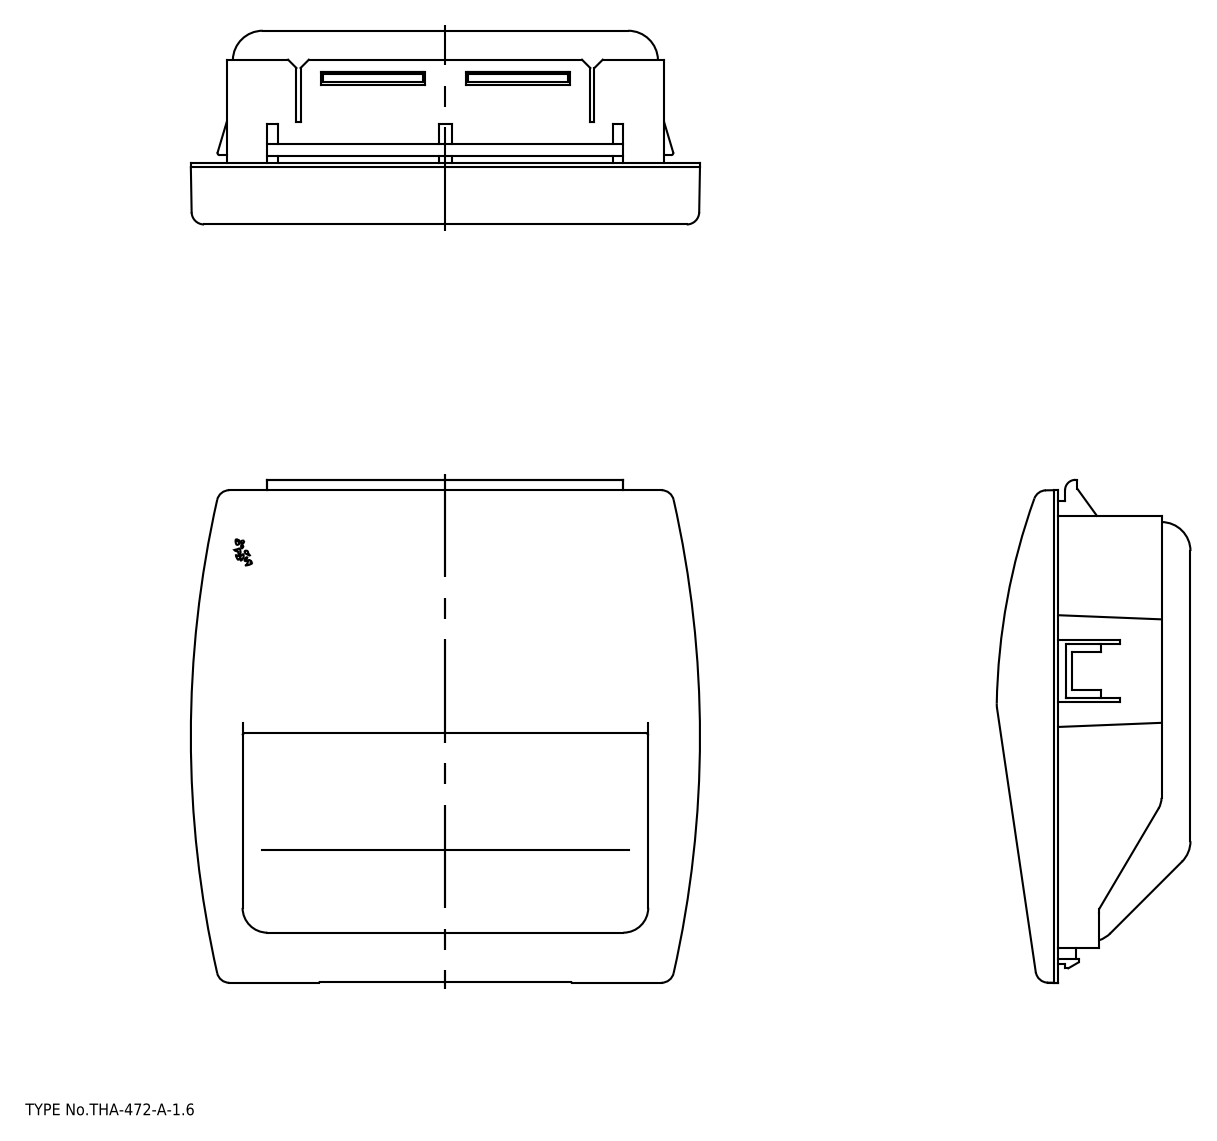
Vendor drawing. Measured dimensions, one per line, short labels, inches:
name: 0020; j10488b0010 2020-03-24; J10488B0030
written by: spGate 16.7.1 (AUTOMOTIVE_DESIGN)
unit: in
bodies: 3 solids, 703 faces (275 planar, 264 cylindrical, 164 other)
size: 4.843 × 4.783 × 1.843
volume: 6.563 in³; area: 158.7 in²
holes: 2× ⌀0.134
rounds: 112× R0.02, 23× R0.039, 21× R0.276, 14× R0.197, 11× R0.012, 8× R0.335, 4× R0.024, 4× R0.118
face distances: 0.079, 4.102, 0.059, 0.138, 3.965, 4.043, 4.024, 1.26, 1.181, 3.886
hole spacings: 2.047
